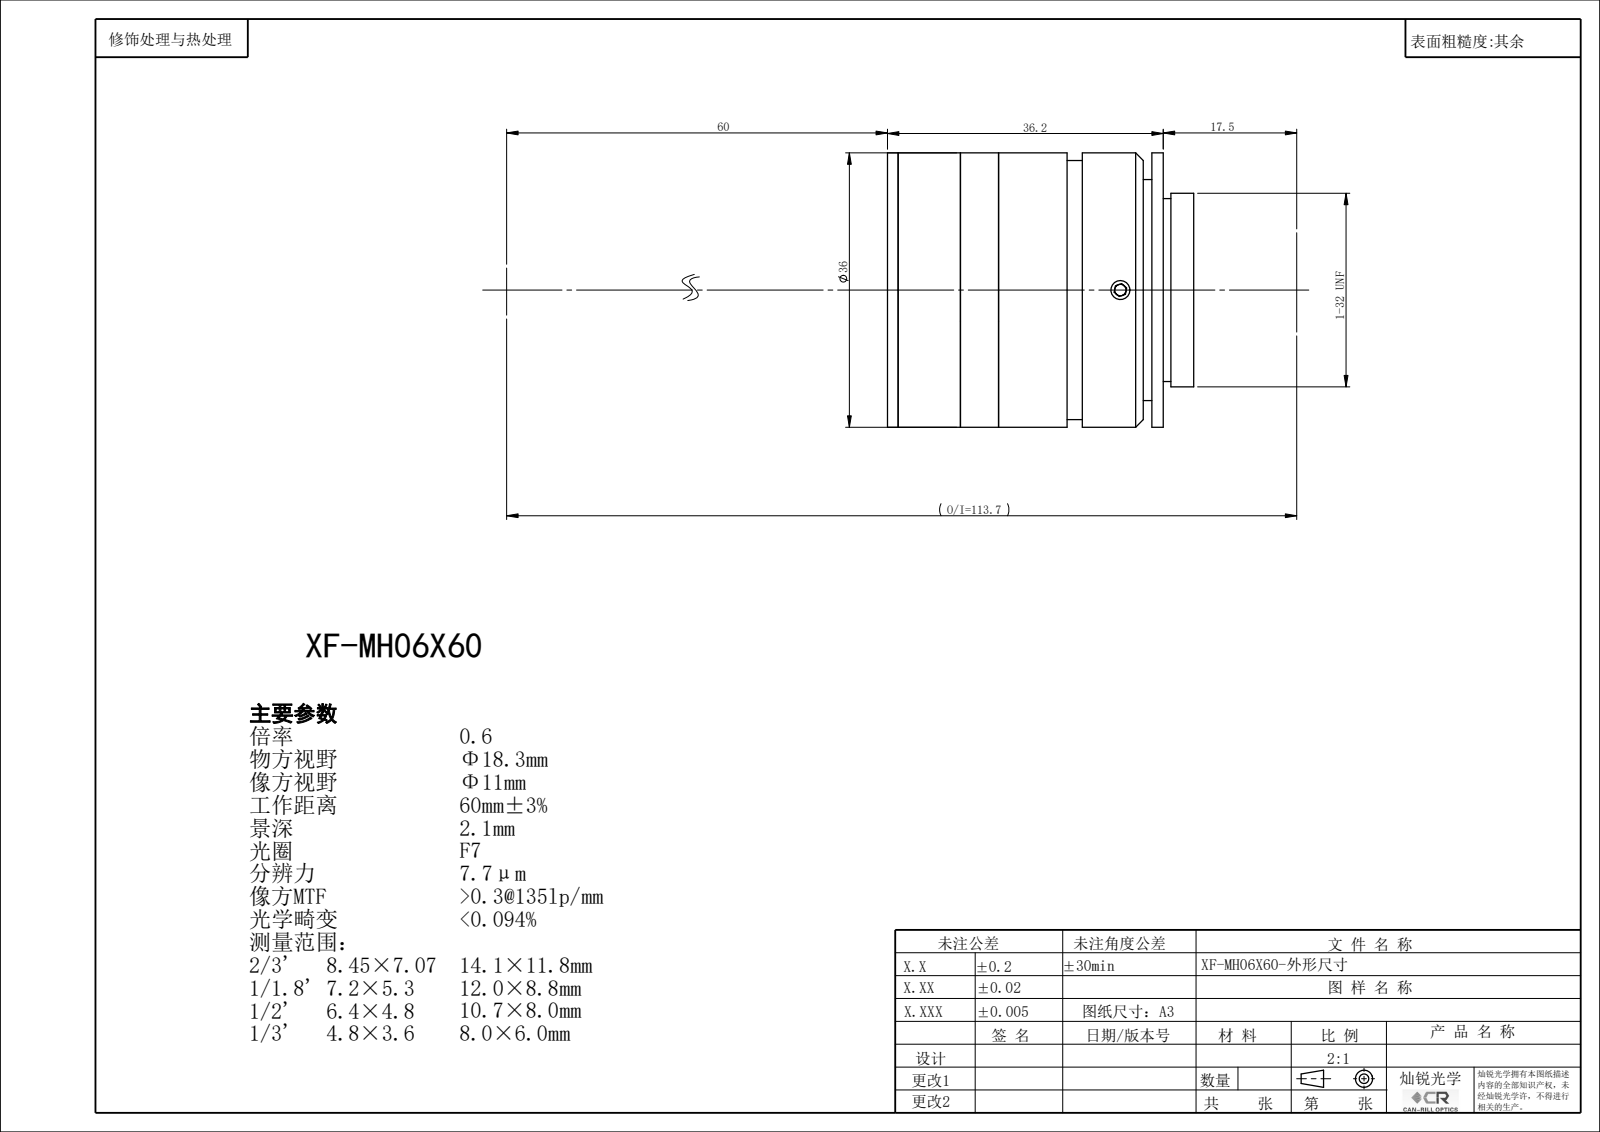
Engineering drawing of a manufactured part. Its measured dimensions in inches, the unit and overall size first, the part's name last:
Units: inches
Overall size (bounding box): 1.583 × 1.417 × 1.417
Round holes (diameter × count): ⌀0.098 ×3, ⌀0.354 ×1, ⌀0.512 ×1, ⌀0.669 ×1, ⌀0.787 ×1, ⌀0.827 ×1, ⌀0.846 ×1, ⌀0.98 ×1, ⌀1.024 ×1
Round bosses / shafts (diameter × count): ⌀1.417 ×1, ⌀1.339 ×1, ⌀1 ×1, ⌀0.945 ×1
Main face-to-face distances: 0.322, 0.519, 0.197, 1.37, 1.048, 0.851, 0.055, 0.378, 0.574, 1.426
Bodies: 0 solids, 93 faces (45 planar, 40 cylindrical, 8 other)
Part name (STEP PRODUCT): XF-MH06X60
STEP written by: SolidWorks 2022 (CONFIG_CONTROL_DESIGN)
